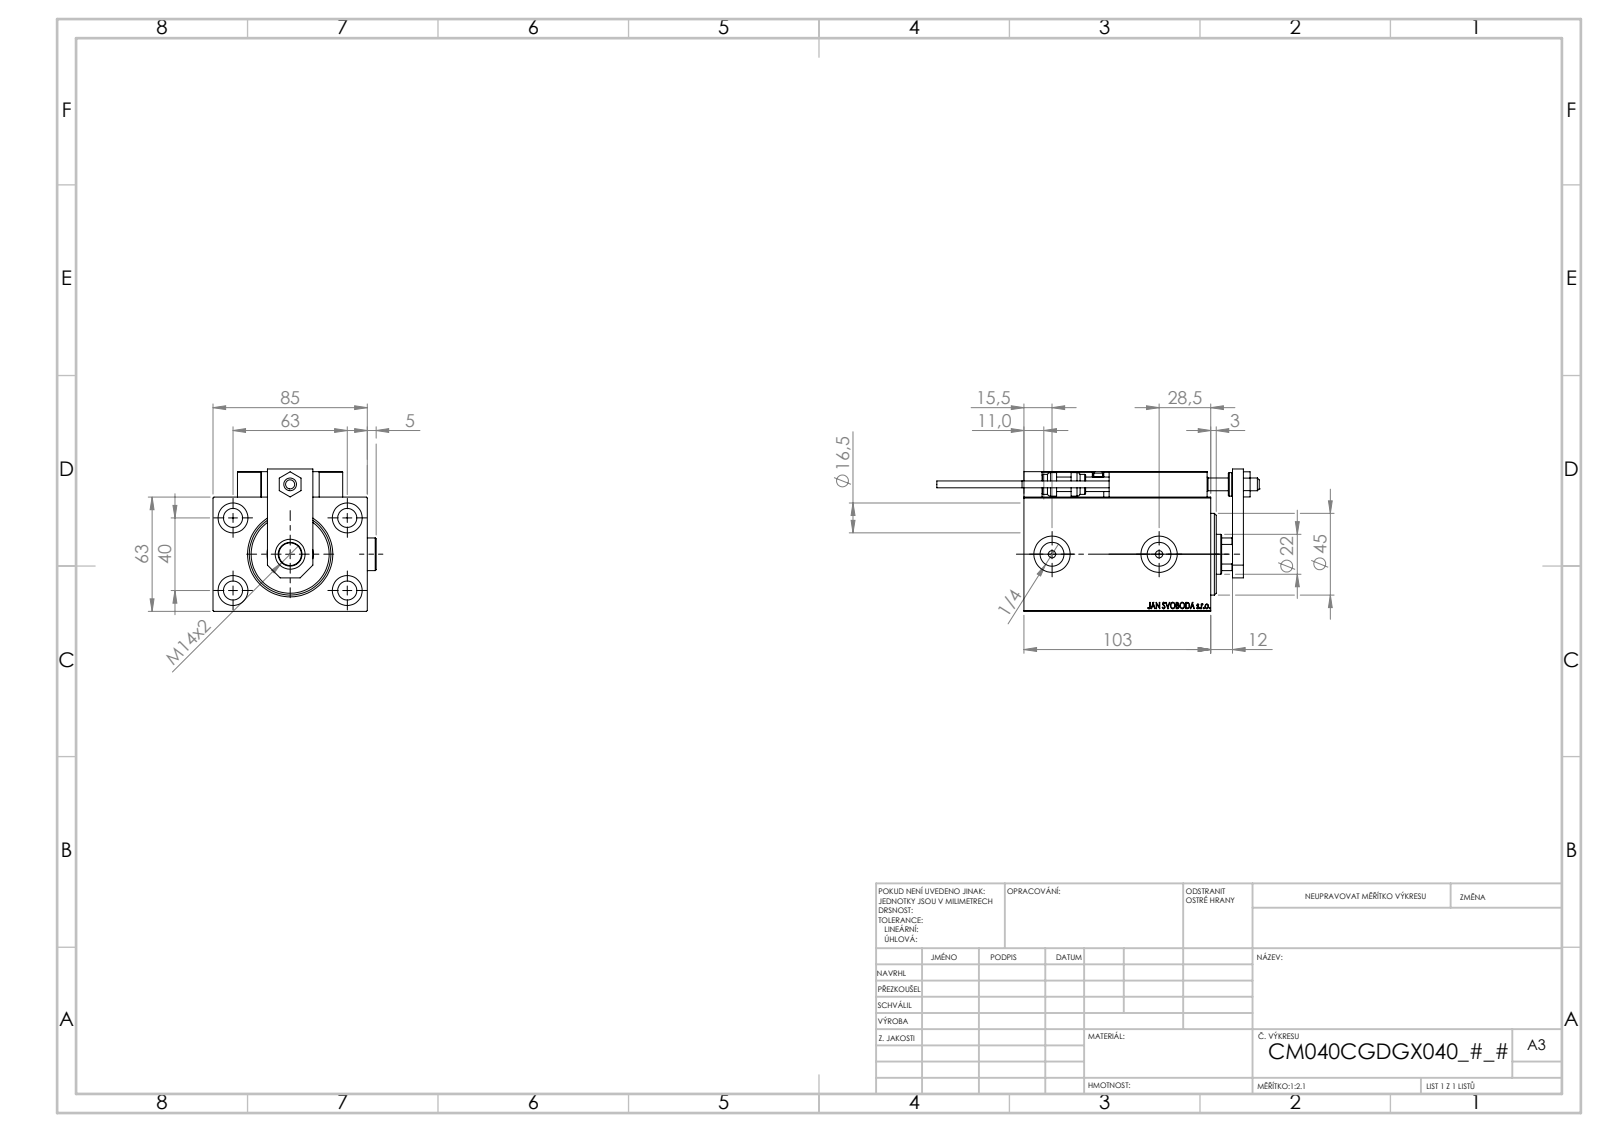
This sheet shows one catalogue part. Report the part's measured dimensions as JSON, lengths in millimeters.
{"part_name": "KONCOVKA; V450CM_VC_B; SWITCH_X_FRONT_BACK; TYC_L79 (+8 more)", "step_written_by": "SolidWorks 2019 (CONFIG_CONTROL_DESIGN)", "units": "millimeters", "bodies": {"solids": 25, "faces": 1336, "planar": 594, "cylindrical": 204, "other": 538}, "overall_size": [177.7, 89.9, 78.5], "volume_mm3": 518564, "surface_area_mm2": 114496, "round_holes": [[4, 6], [8, 5], [16.5, 5], [3.2, 4], [10.5, 4], [5, 2], [13.16, 2], [20, 2], [7, 1], [12.5, 1], [22, 1], [25.5, 1]], "round_bosses_or_shafts": [[18, 2], [5, 2], [3.8, 2], [13, 1], [11, 1]], "partial_cylinders_radius": [[0.3, 30], [3, 2], [10.5, 1]], "face_to_face_distances": [63, 85, 12, 91, 103, 14, 77, 15, 18, 3], "hole_center_spacings": [37.31, 11.37, 20, 29.59, 29.69, 36.06, 36.53, 40]}
